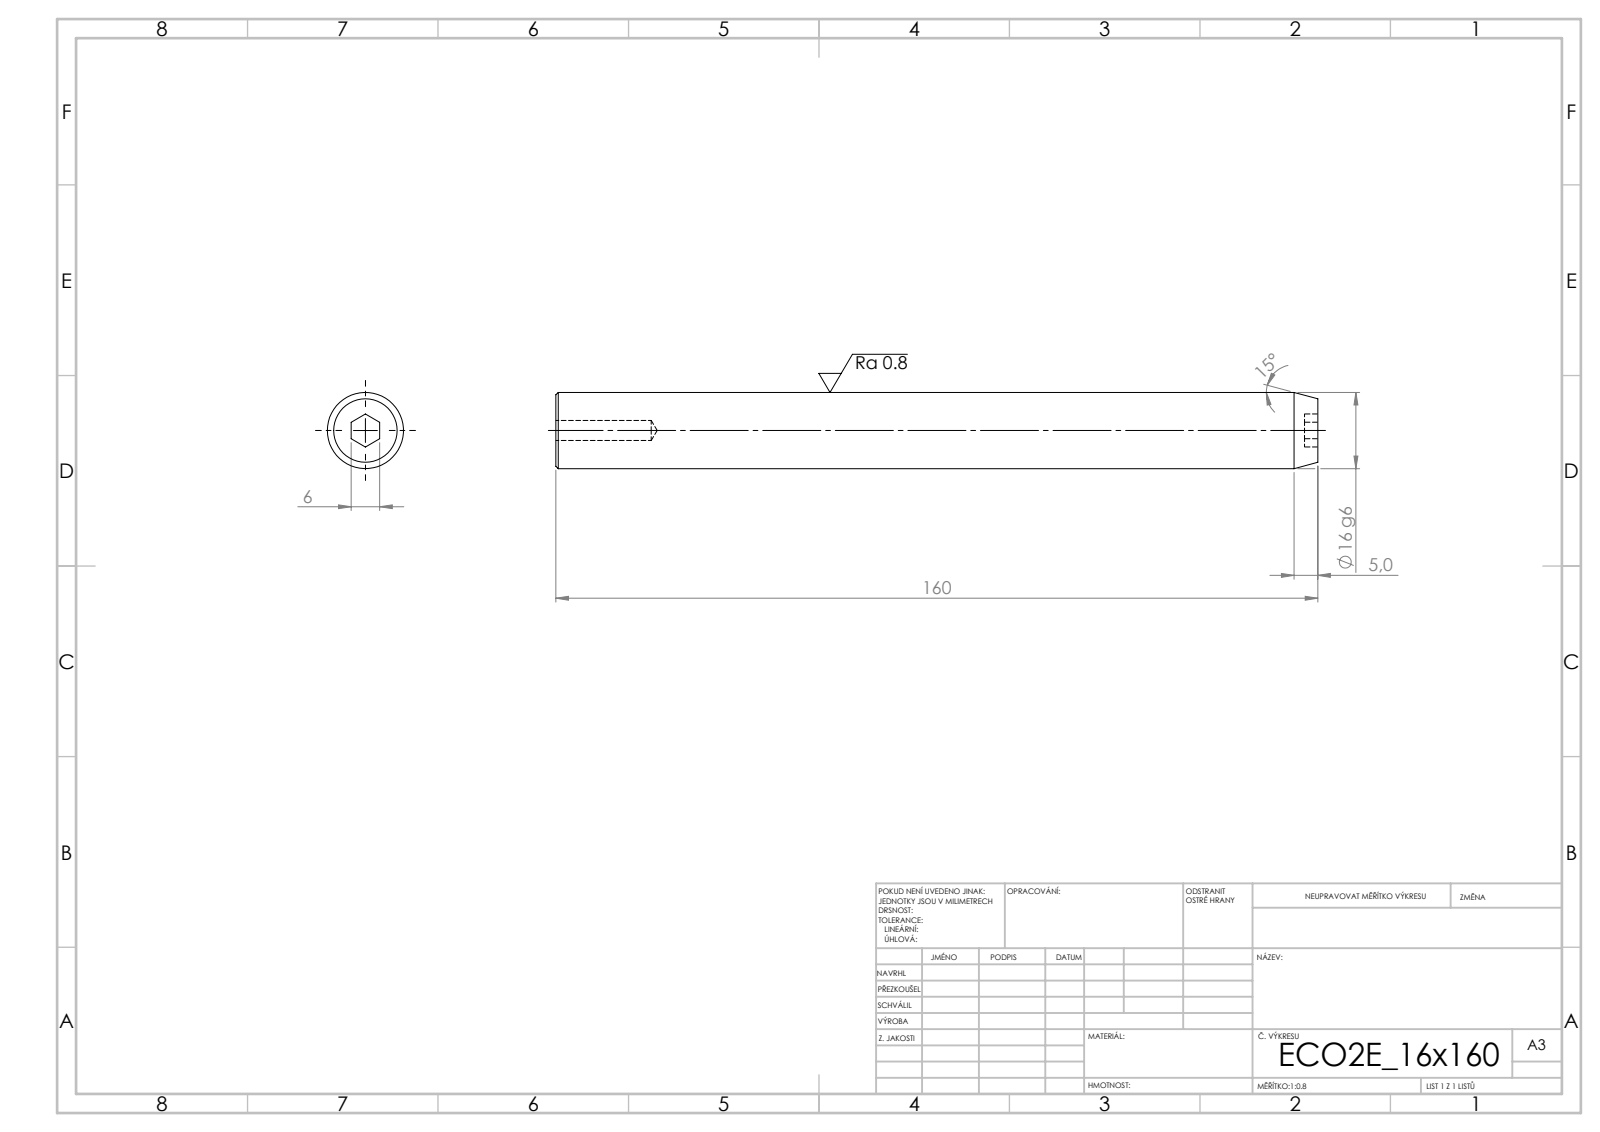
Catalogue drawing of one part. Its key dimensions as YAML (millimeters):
step_written_by: "SolidWorks 2019 (CONFIG_CONTROL_DESIGN)"
units: millimeters
bodies: {solids: 1, faces: 19, planar: 9, cylindrical: 4, other: 6}
overall_size: [160, 16, 16]
volume: 31635
surface_area: 8679
round_holes:
  - {diameter: 4.2, count: 1}
round_bosses_or_shafts:
  - {diameter: 16, count: 1}
face_to_face_distances: [160, 2.8, 157.2, 6]
